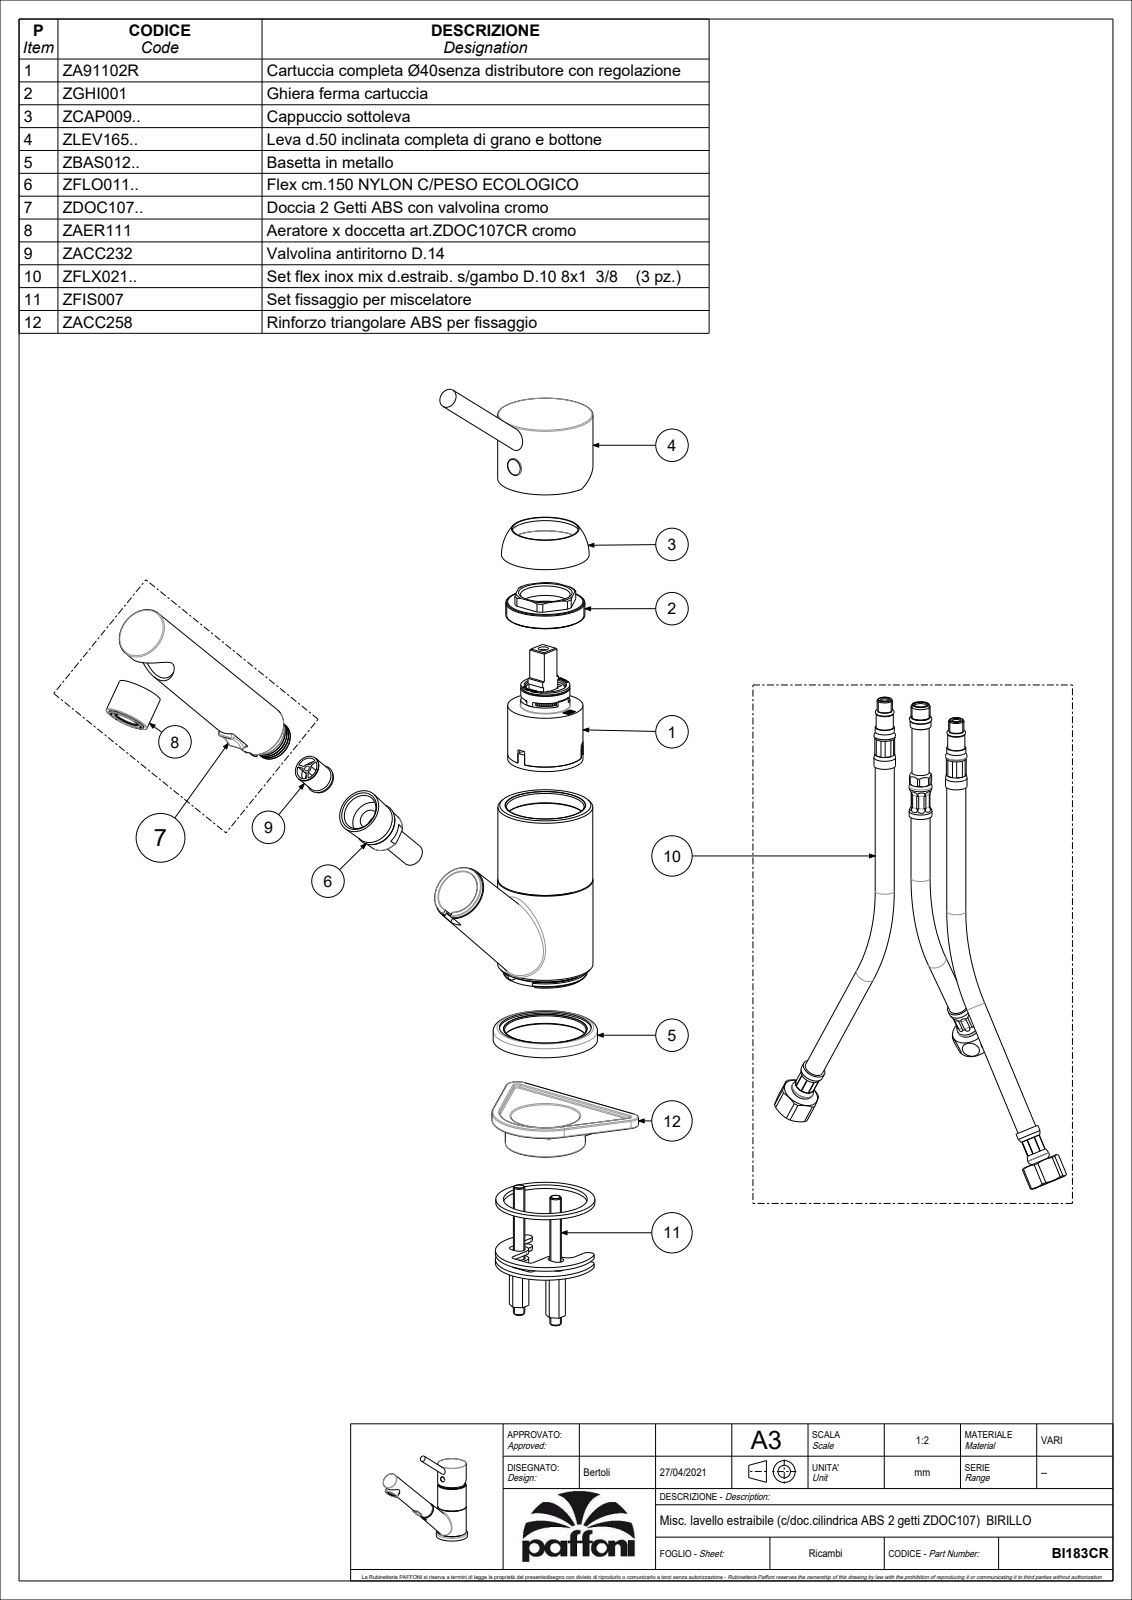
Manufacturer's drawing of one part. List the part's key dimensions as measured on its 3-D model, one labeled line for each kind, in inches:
Part name (STEP PRODUCT): BI183CR
STEP written by: CREO PARAMETRIC BY PTC INC, 2020044 (CONFIG_CONTROL_DESIGN)
Units: inches
Bodies: 1 solid, 1334 faces (640 planar, 372 cylindrical, 322 other)
Overall size (bounding box): 8.058 × 6.683 × 2.154
Volume: 12.16 in³ · Surface area: 199.4 in²
Round holes (diameter × count): ⌀0.276 ×5, ⌀0.13 ×2, ⌀0.217 ×2, ⌀0.315 ×2, ⌀0.339 ×2, ⌀0.37 ×2, ⌀0.433 ×2, ⌀0.461 ×2, ⌀0.118 ×1, ⌀0.157 ×1, ⌀0.165 ×1, ⌀0.197 ×1
Round bosses / shafts (diameter × count): ⌀2.154 ×1, ⌀1.969 ×1, ⌀1.961 ×1, ⌀1.89 ×1, ⌀1.764 ×1, ⌀1.76 ×1, ⌀1.732 ×1, ⌀1.654 ×1
Partial cylindrical surfaces — rounded edges, fillets, slot ends (radius × count): R0.008 ×50, R0.02 ×24, R0.039 ×14, R0.012 ×5, R0.295 ×2, R0.354 ×2, R0.492 ×2, R0.057 ×1
Main face-to-face distances: 2.555, 1.791, 0.122, 0.425, 0.843, 0.02, 1.713, 0.72, 1.835, 0.823
Hole centre spacings: 0.443, 0.021, 0.209, 0.217, 0.343, 0.348, 0.379, 0.382
